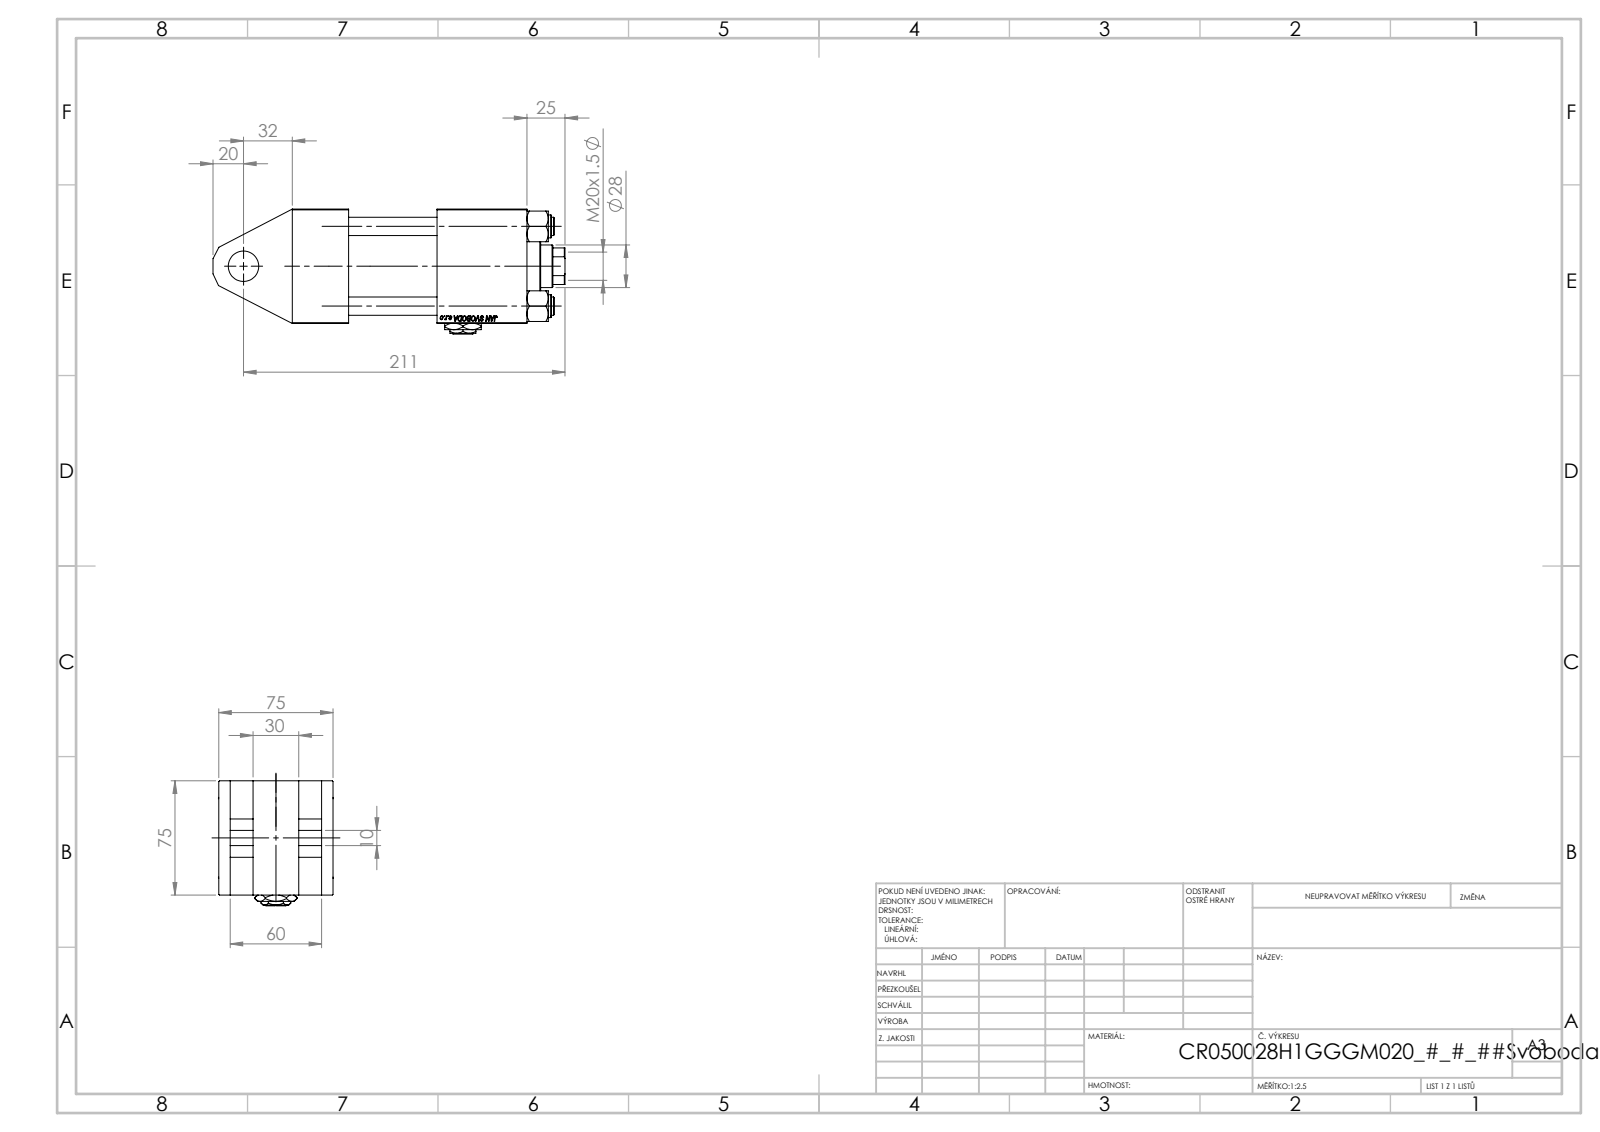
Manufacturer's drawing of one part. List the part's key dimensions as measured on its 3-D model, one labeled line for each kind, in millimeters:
Part name (STEP PRODUCT): V215CR_TYCINKA_H; V215_VC_A; V215CR_H_Body; Zatka_pro_OIL_PORT (+2 more)
STEP written by: SolidWorks 2019 (CONFIG_CONTROL_DESIGN)
Units: millimetres
Bodies: 12 solids, 1175 faces (541 planar, 86 cylindrical, 548 other)
Overall size (bounding box): 231 × 82 × 75.54
Volume: 742 950 mm³ · Surface area: 168 485 mm²
Round holes (diameter × count): ⌀12 ×4, ⌀7 ×2, ⌀20.96 ×2, ⌀30 ×2, ⌀18.5 ×1, ⌀20 ×1, ⌀28 ×1, ⌀31 ×1, ⌀41 ×1, ⌀50 ×1, ⌀53 ×1
Round bosses / shafts (diameter × count): ⌀15 ×4, ⌀56 ×1, ⌀42 ×1
Partial cylindrical surfaces — rounded edges, fillets, slot ends (radius × count): R13.5 ×1
Main face-to-face distances: 75, 67.5, 7.5, 22.5, 52.5, 15, 45, 117, 95, 37
Hole centre spacings: 36.98, 52.3, 73.96, 93.5
